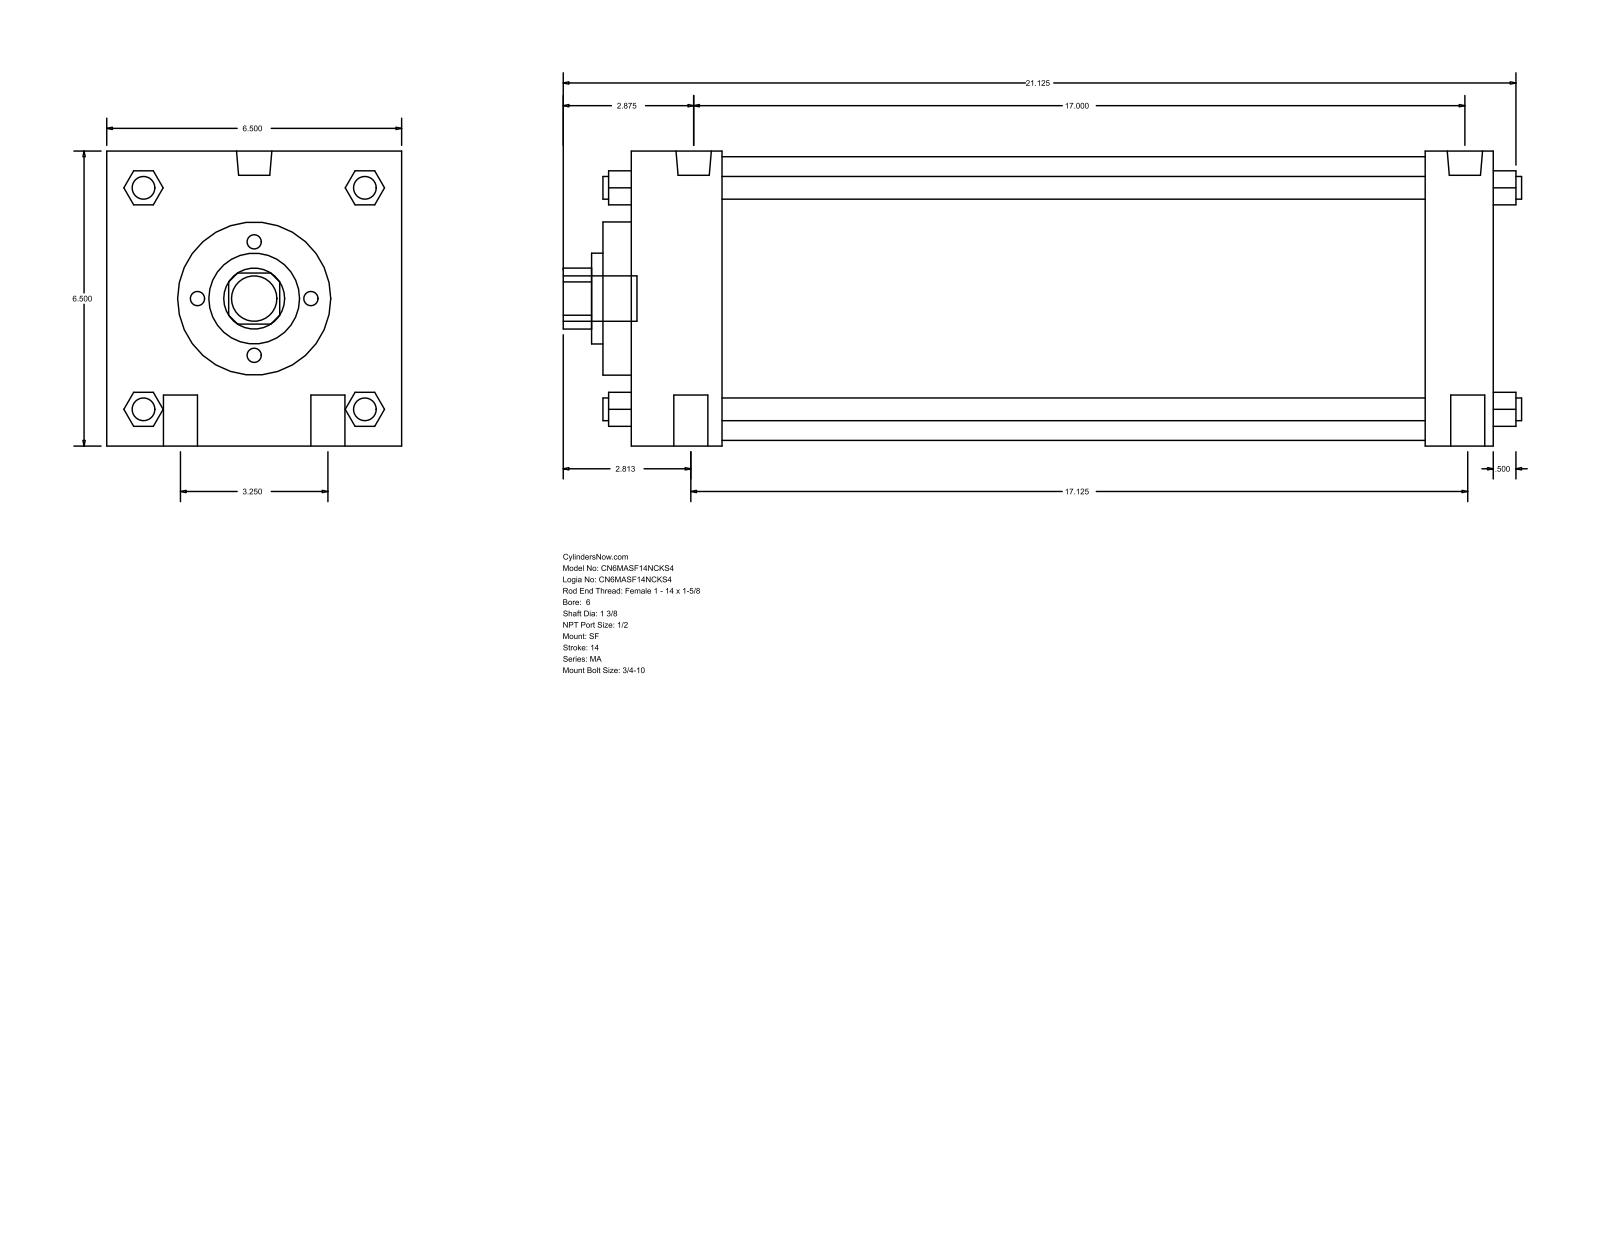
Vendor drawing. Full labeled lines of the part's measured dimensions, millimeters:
Part name (STEP PRODUCT): MA_SF__0600_1.375
STEP written by: GSSL Pune (CONFIG_CONTROL_DESIGN)
Units: millimetres
Bodies: 0 solids, 126 faces (95 planar, 31 cylindrical, 0 other)
Overall size (bounding box): 536.58 × 165.1 × 165.1
Round holes (diameter × count): ⌀34.92 ×1, ⌀50.8 ×1, ⌀85.72 ×1, ⌀158.75 ×1
Round bosses / shafts (diameter × count): ⌀19.05 ×4, ⌀12.7 ×4, ⌀19.77 ×2, ⌀17.46 ×2, ⌀25.4 ×1
Partial cylindrical surfaces — rounded edges, fillets, slot ends (radius × count): R17.06 ×1
Main face-to-face distances: 165.1, 482.6, 444.5, 50.8, 38.1, 393.7, 431.8, 15.87, 66.67, 460.37
